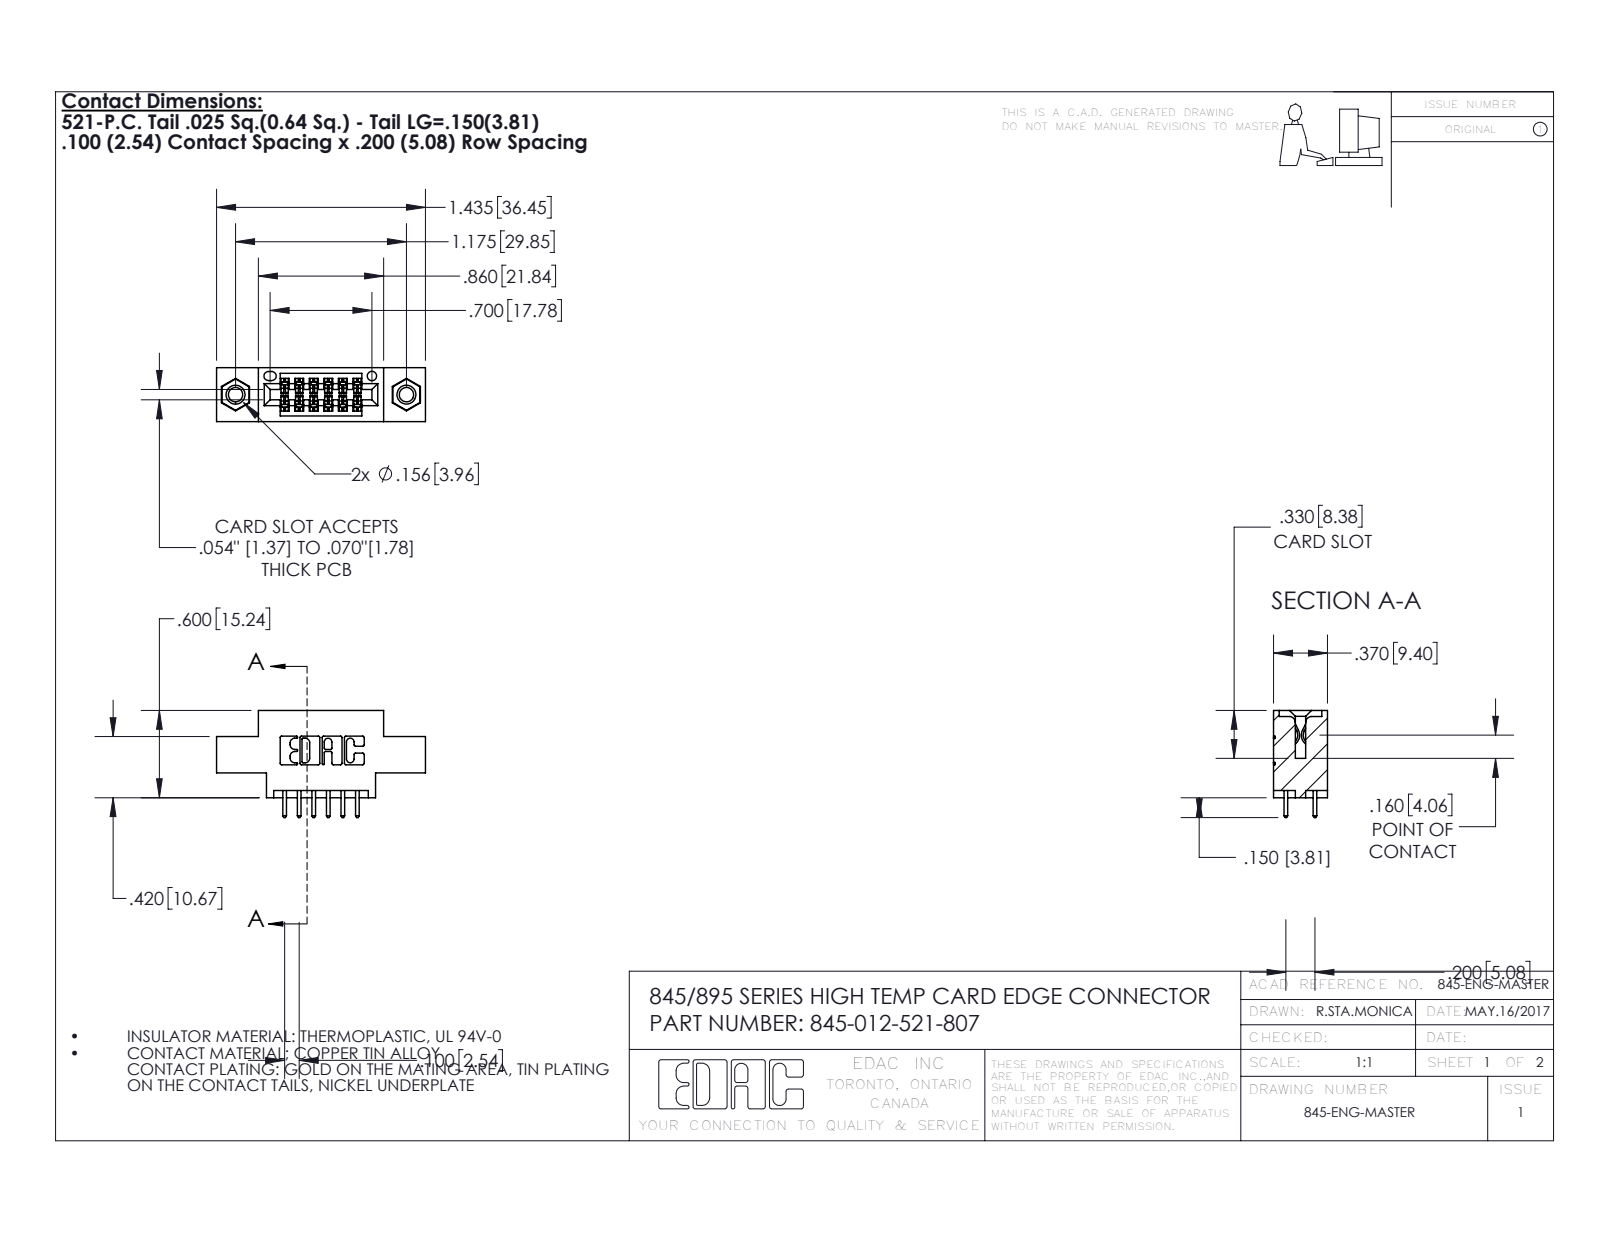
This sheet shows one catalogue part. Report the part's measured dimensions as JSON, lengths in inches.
{"part_name": "345-250-001_345-250-005-103; 345 Part_0.170 Offset - 0.156 Dia-TI; 345-292-001_345-293-121; 345-012-521-807", "step_written_by": "SolidWorks 2016 (CONFIG_CONTROL_DESIGN)", "units": "inches", "bodies": {"solids": 15, "faces": 790, "planar": 512, "cylindrical": 262, "other": 16}, "overall_size": [1.435, 0.737, 0.37], "volume_in3": 0.188, "surface_area_in2": 6.18, "round_holes": [[0.098, 2], [0.125, 2], [0.156, 2], [0.064, 1]], "round_bosses_or_shafts": [[0.155, 2]], "partial_cylinders_radius": [[0.01, 22], [0.006, 18], [0.01, 12], [0.007, 6], [0.031, 6], [0.026, 3], [0.014, 2], [0.019, 2]], "face_to_face_distances": [0.2, 0.37, 0.072, 0.298, 0.1, 0.025, 0.098, 0.272, 0.225, 0.06], "hole_center_spacings": [0.27, 0.946, 1.175]}
